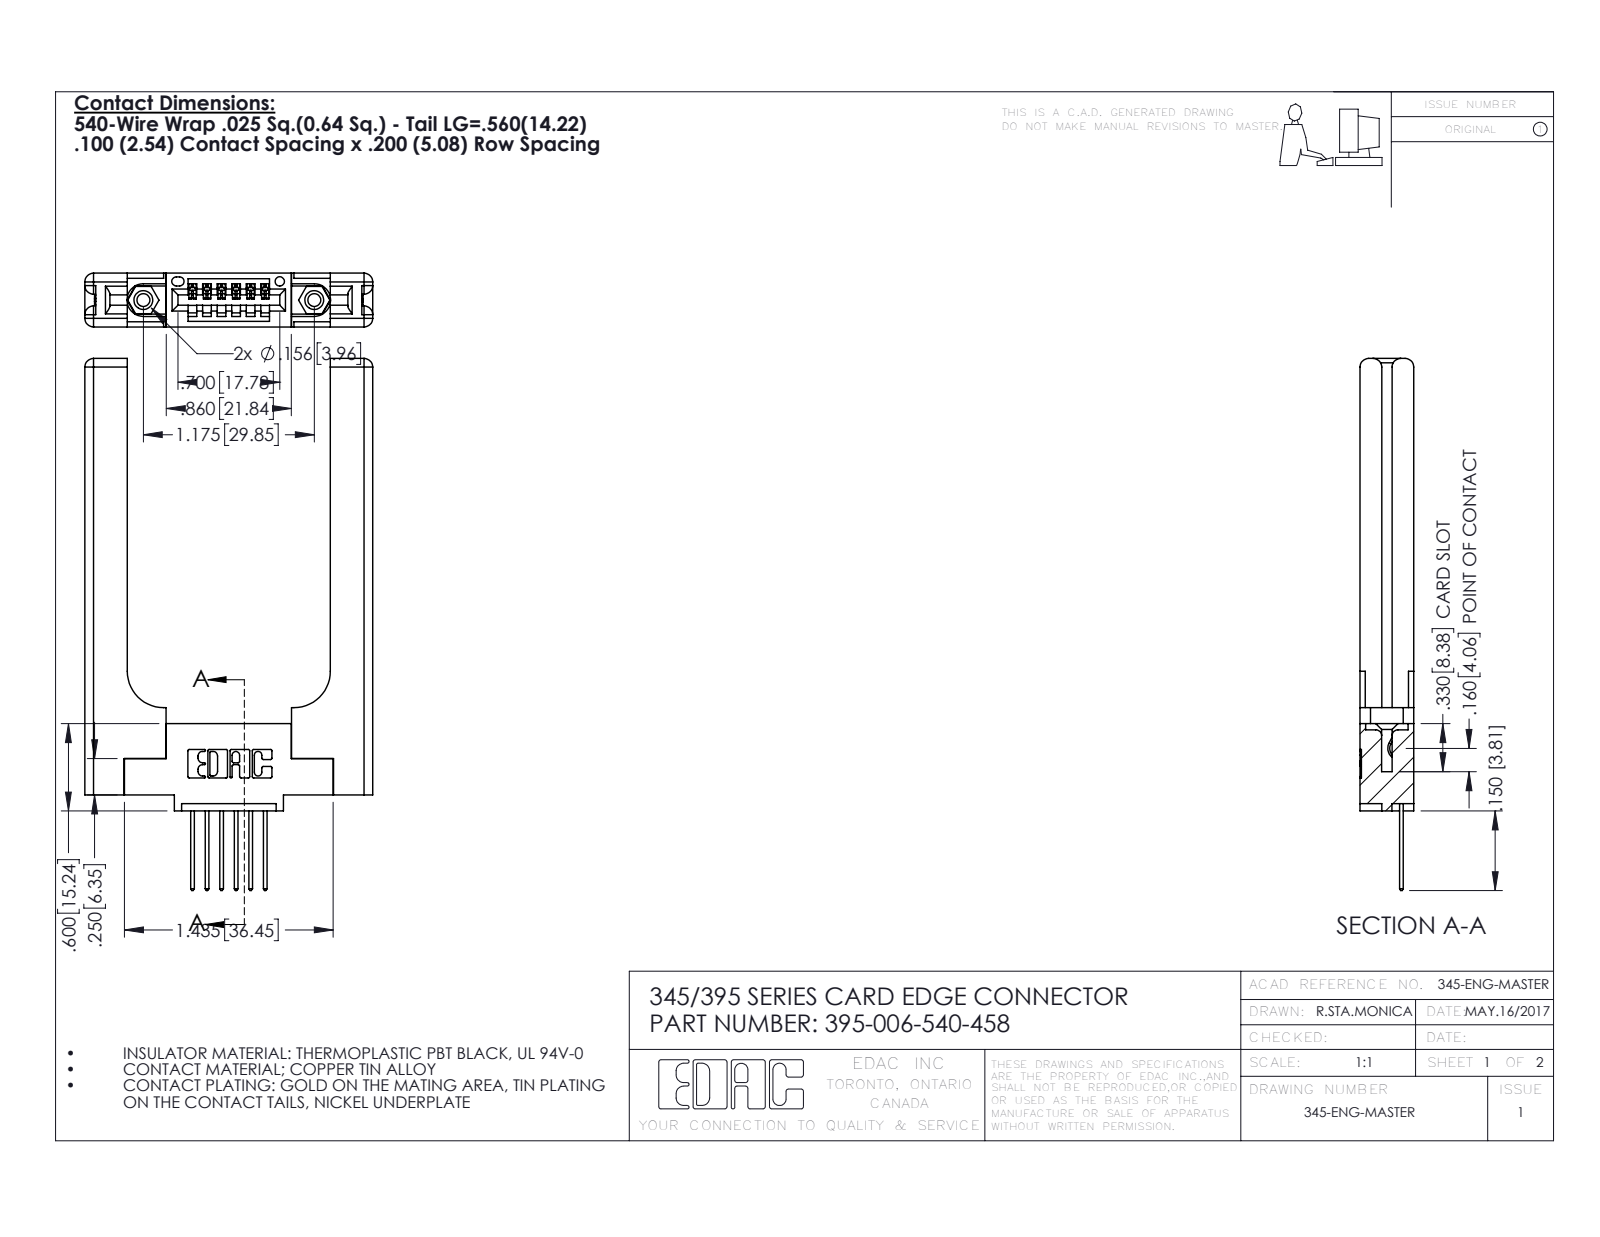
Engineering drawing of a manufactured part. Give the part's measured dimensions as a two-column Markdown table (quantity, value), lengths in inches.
| quantity | value |
| --- | --- |
| part name | 345-292-001_345-293-140; 345 Part_0.110 Offset - 0.156 Dia-TH; 345-250-001_345-250-001-102; 345-220-058_345-220-058 (+1 more) |
| STEP written by | SolidWorks 2016 (CONFIG_CONTROL_DESIGN) |
| units | inches |
| bodies | 11 solids, 734 faces (472 planar, 202 cylindrical, 60 other) |
| overall size | 3.657 × 1.979 × 0.37 |
| volume | 0.788 in³ |
| surface area | 16.78 in² |
| round holes (diameter × count) | 0.089 × 2, 0.125 × 2, 0.156 × 2, 0.064 × 1 |
| round bosses / shafts (diameter × count) | 0.155 × 2 |
| partial cylindrical surfaces (radius × count) | 0.01 × 22, 0.06 × 16, 0.006 × 12, 0.01 × 12, 0.007 × 6, 0.031 × 6, 0.026 × 3, 0.03 × 2 |
| main face-to-face distances | 0.37, 0.15, 0.22, 0.072, 0.148, 0.077, 1.396, 0.298, 0.071, 0.292 |
| hole center spacings | 0.27, 0.946, 1.175 |
